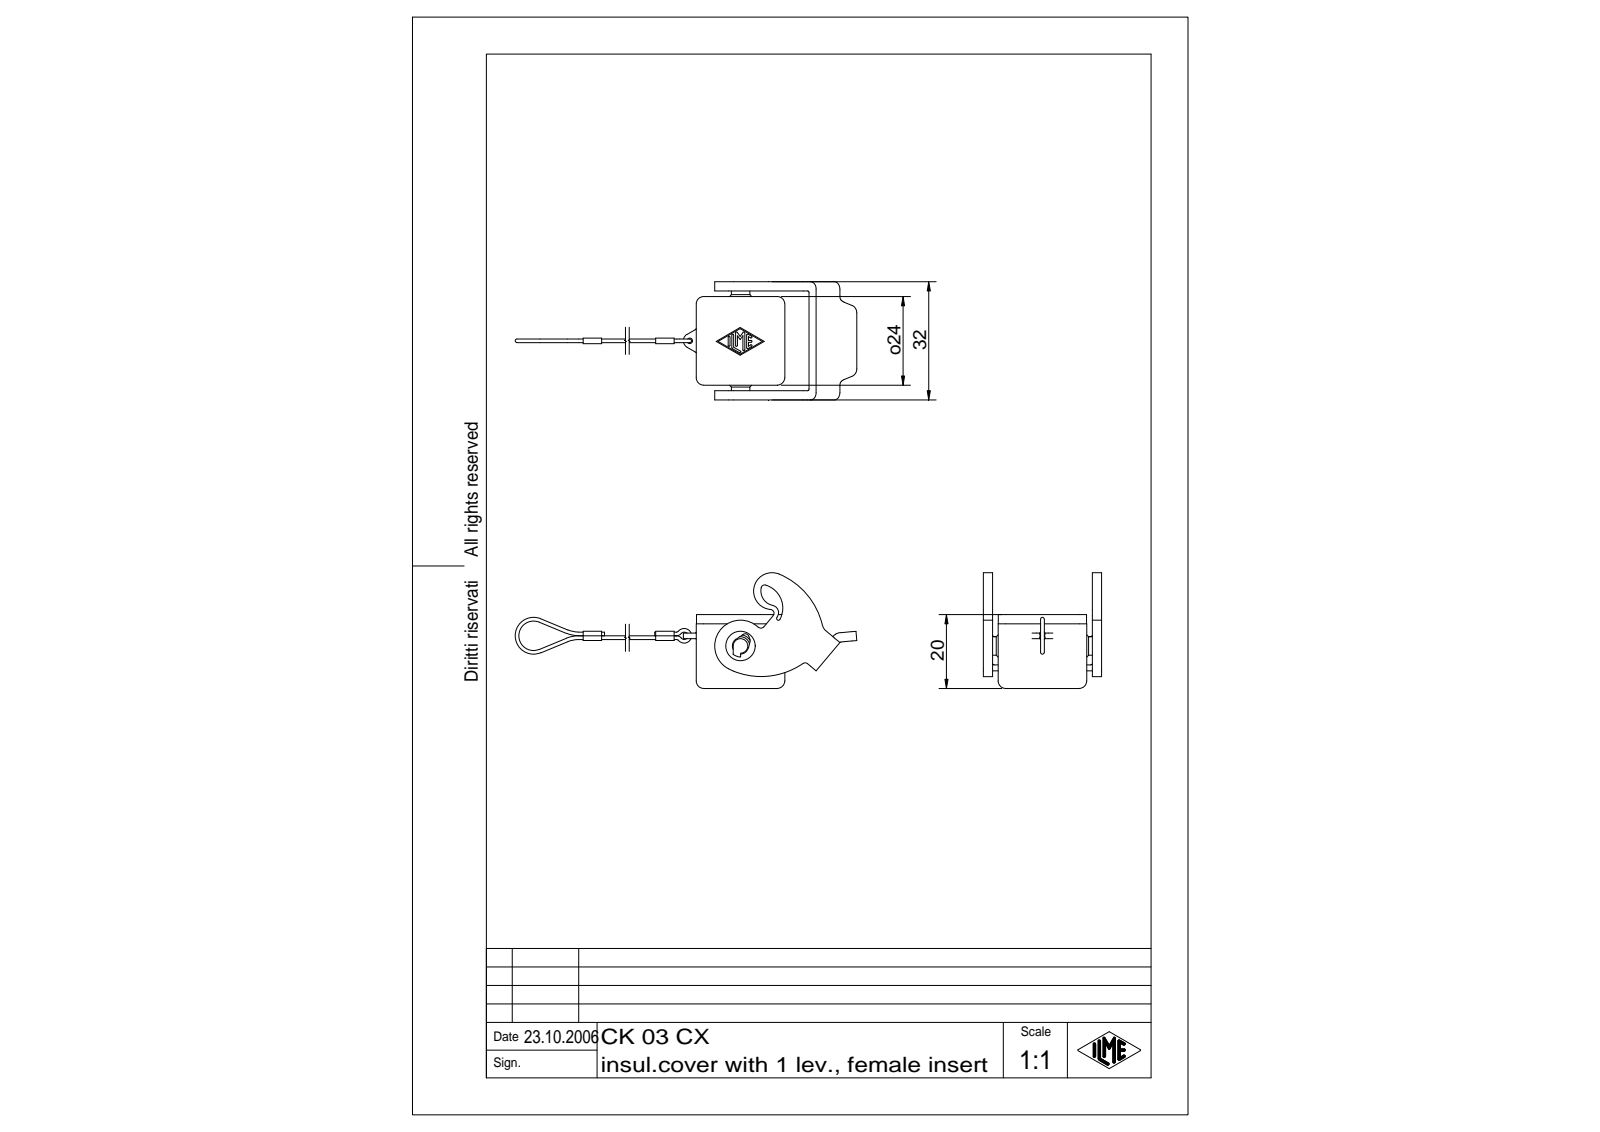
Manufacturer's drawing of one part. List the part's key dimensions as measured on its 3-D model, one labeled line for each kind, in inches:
Part name (STEP PRODUCT): CK 03 CX
STEP written by: Autodesk Inventor 7 (AUTOMOTIVE_DESIGN)
Units: inches
Bodies: 2 solids, 361 faces (94 planar, 170 cylindrical, 97 other)
Overall size (bounding box): 4.562 × 1.26 × 1.234
Volume: 0.442 in³ · Surface area: 13.53 in²
Round holes (diameter × count): ⌀0.059 ×1, ⌀0.315 ×1
Round bosses / shafts (diameter × count): ⌀0.039 ×4, ⌀0.197 ×1, ⌀0.157 ×1
Partial cylindrical surfaces — rounded edges, fillets, slot ends (radius × count): R0.079 ×20, R0.02 ×16, R0.01 ×14, R0.008 ×12, R0.039 ×6, R0.004 ×3, R0.03 ×2, R0.118 ×2
Main face-to-face distances: 0.059, 0.098, 0.886, 0.945, 0.827, 0.787, 0.157, 1.004, 0.039, 0.846
